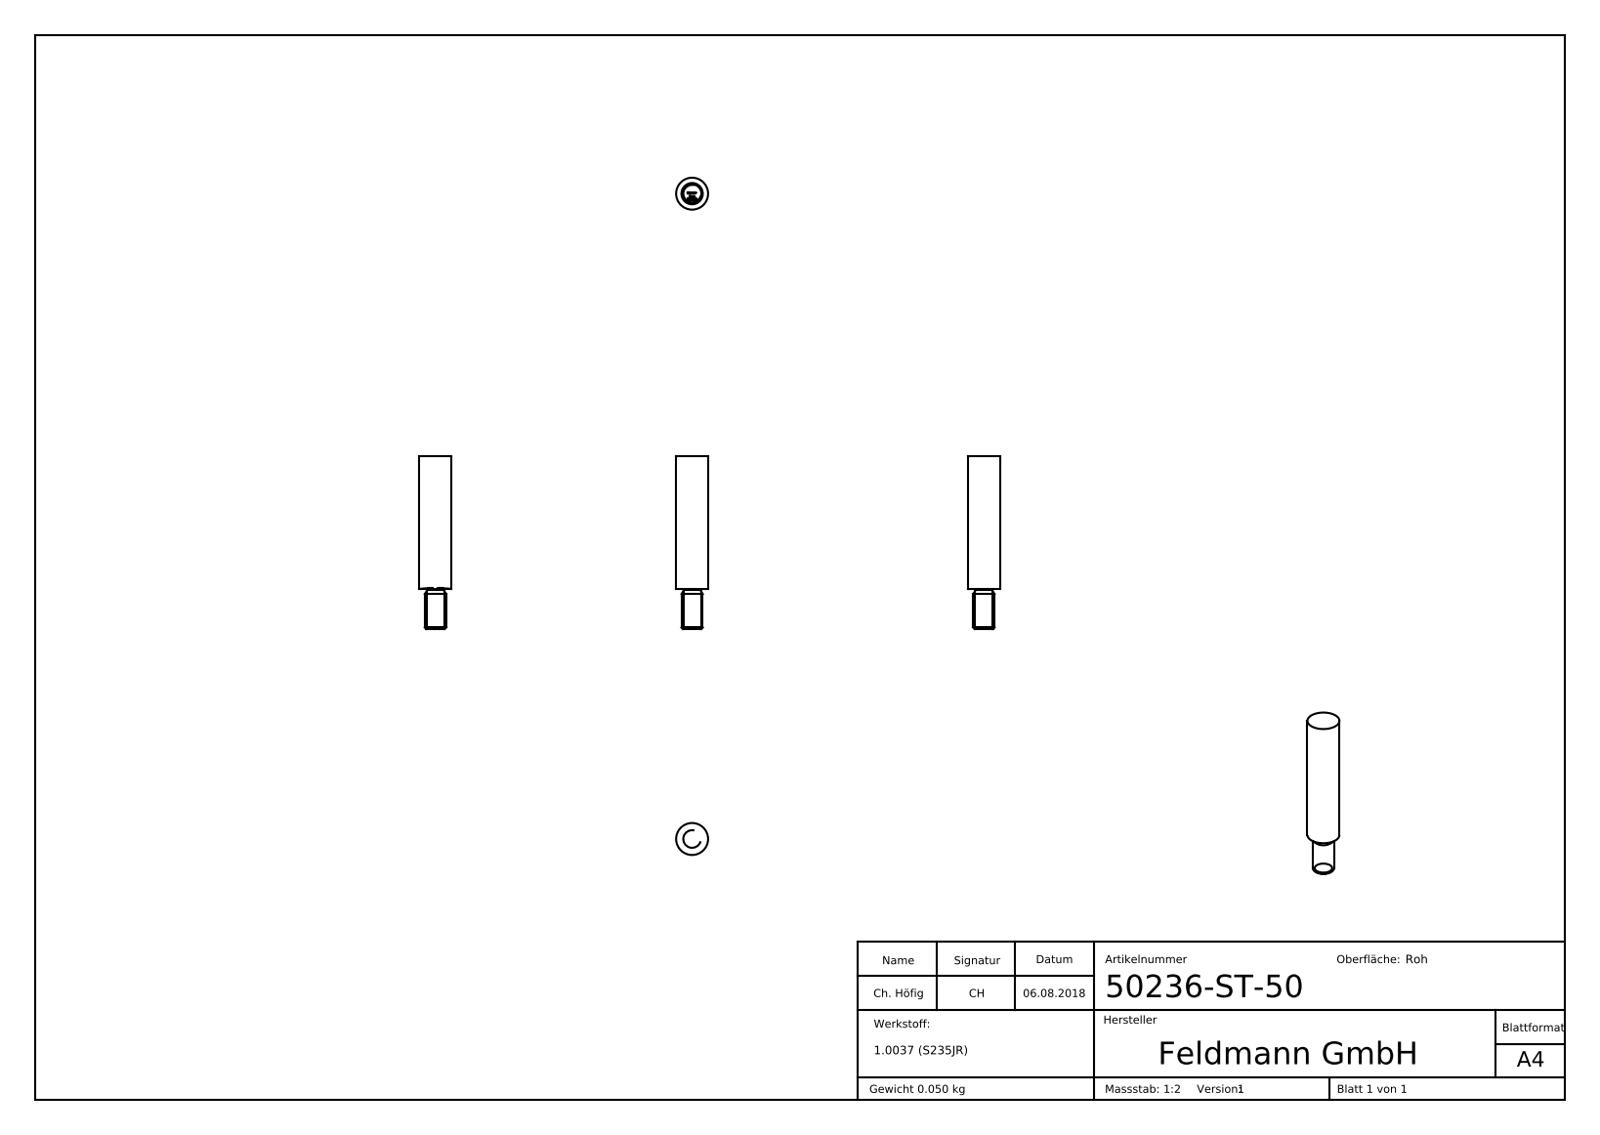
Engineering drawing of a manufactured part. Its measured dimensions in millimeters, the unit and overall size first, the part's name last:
Units: millimetres
Overall size (bounding box): 65 × 12 × 12
Round bosses / shafts (diameter × count): ⌀12 ×1, ⌀8 ×1
Main face-to-face distances: 65, 64.9, 1.1, 2.38, 0.53, 0.46, 2.39, 0.57, 1.05, 0.47
Volume: 6 370 mm³ · Surface area: 2 508 mm²
Bodies: 1 solid, 263 faces (123 planar, 4 cylindrical, 136 other)
Part name (STEP PRODUCT): 50236-ST-50
STEP written by: SolidWorks 2015 (CONFIG_CONTROL_DESIGN)
